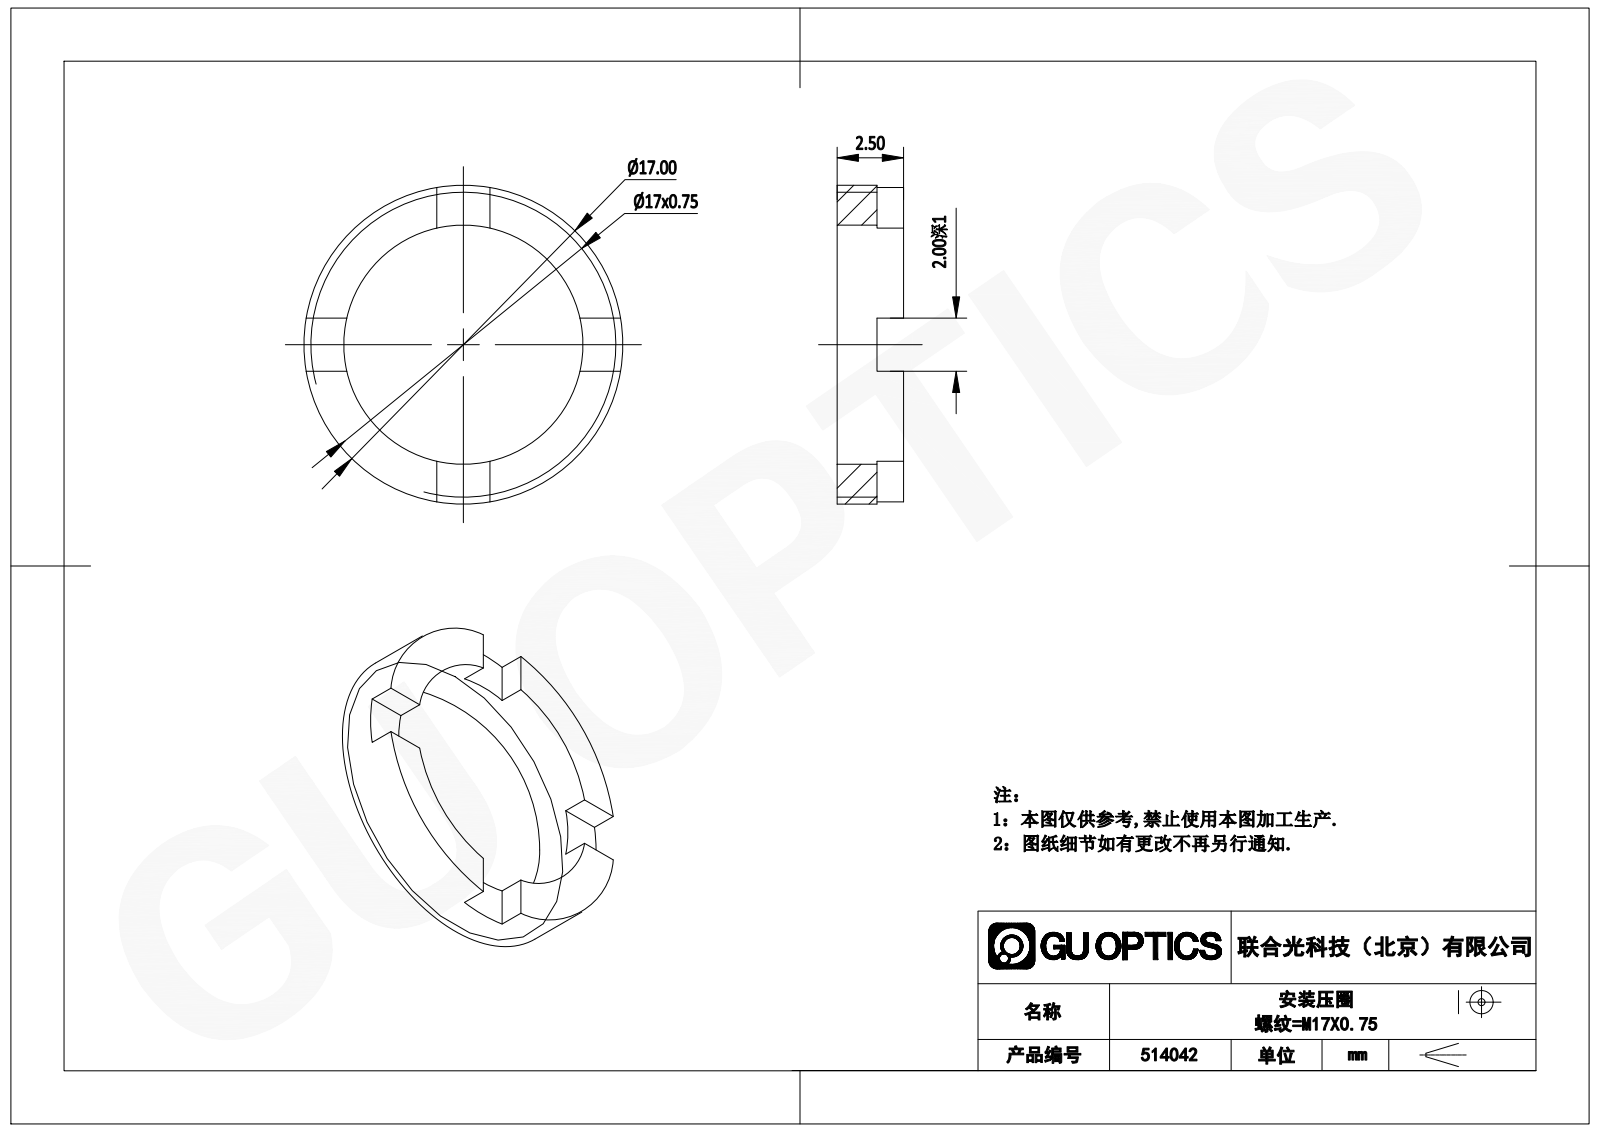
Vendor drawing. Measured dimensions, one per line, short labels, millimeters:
name: 514042
written by: SolidWorks 2020 (CONFIG_CONTROL_DESIGN)
unit: mm
bodies: 1 solid, 21 faces (17 planar, 4 cylindrical, 0 other)
size: 17 × 17 × 2.5
volume: 171 mm³; area: 386 mm²
holes: 1× ⌀14
bosses: 1× ⌀17
face distances: 2.5, 1.5, 1, 2
